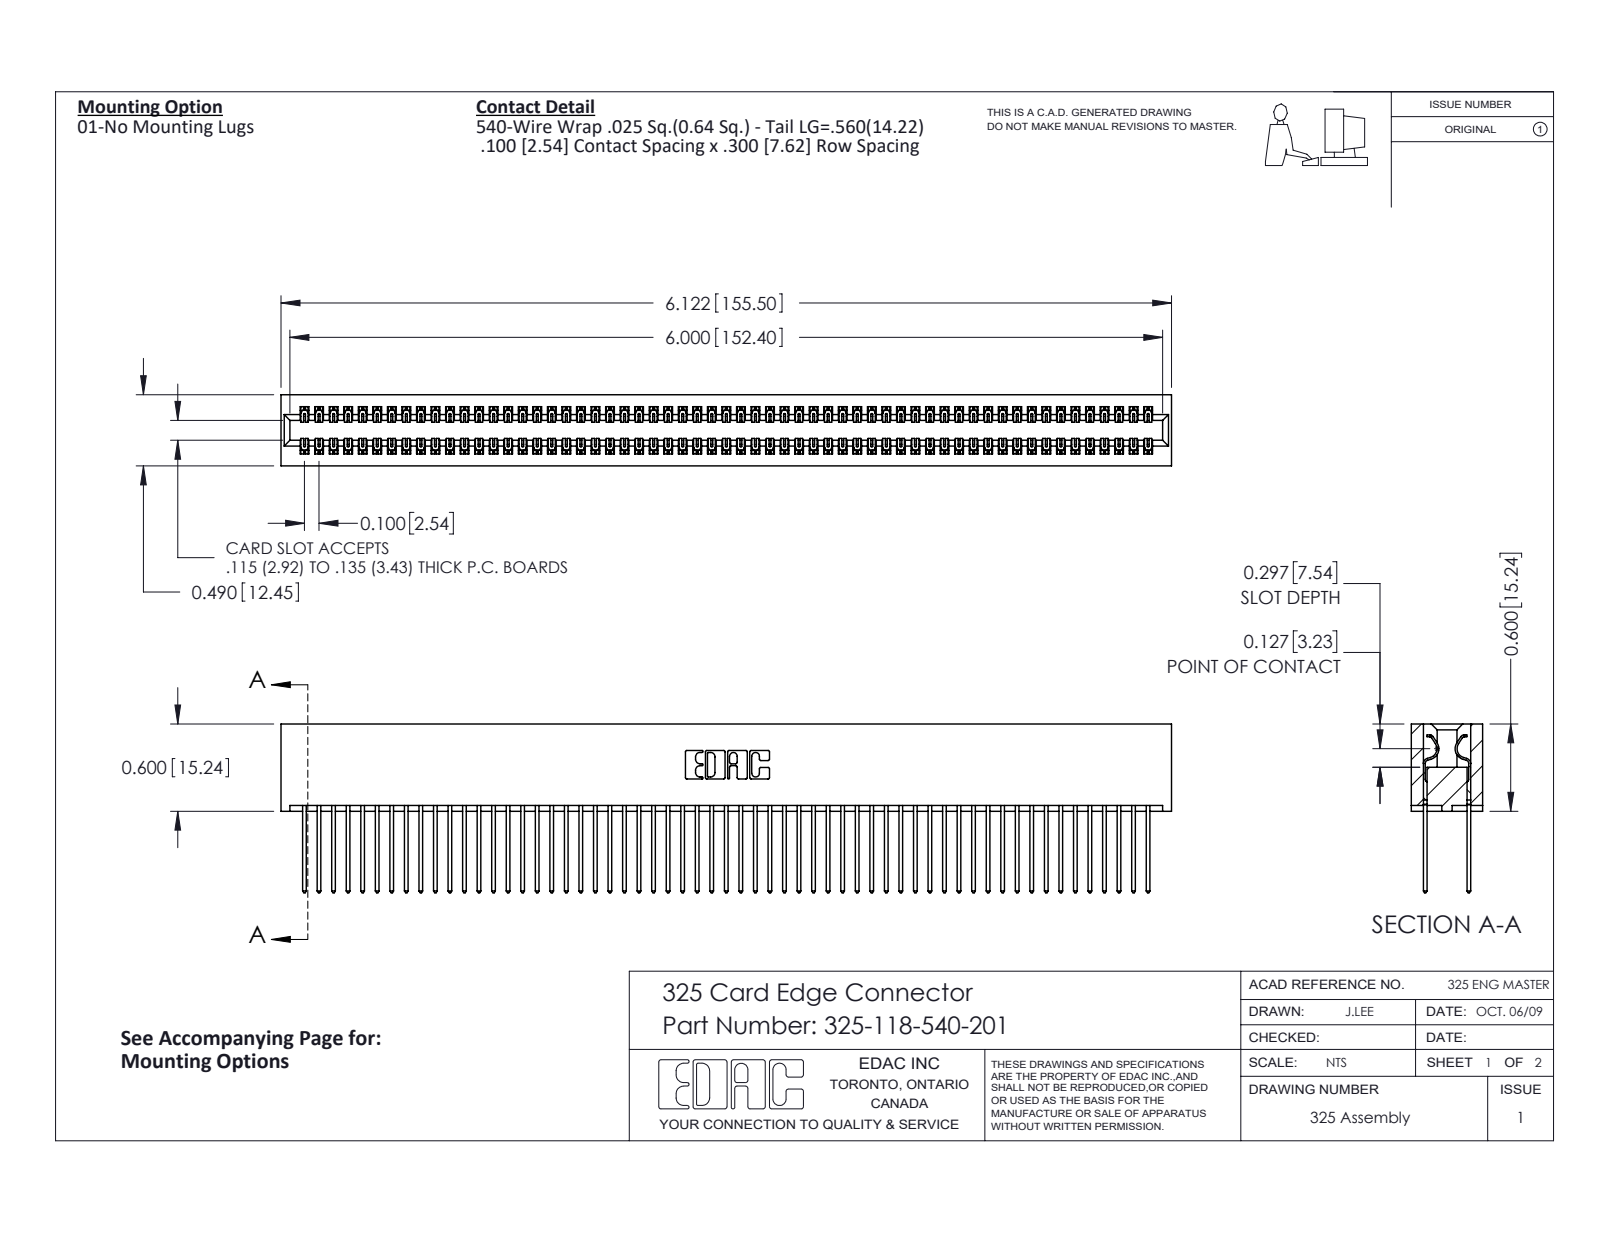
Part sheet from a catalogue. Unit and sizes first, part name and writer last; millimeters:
Units: millimetres
Overall size (bounding box): 155.5 × 29.5 × 12.4
Partial cylindrical surfaces — rounded edges, fillets, slot ends (radius × count): R0.2 ×177, R0.3 ×118, R0.3 ×22, R0.2 ×6, R0.8 ×6, R0.7 ×3, R0.4 ×2, R0.6 ×2
Main face-to-face distances: 2.1, 10.3, 7.6, 2.7, 9.7, 0.6, 8.3, 12.4, 7, 14.2
Volume: 21 290 mm³ · Surface area: 28 950 mm²
Bodies: 119 solids, 6242 faces (4314 planar, 1928 cylindrical, 0 other)
Part name (STEP PRODUCT): 325-118-540-201; 325 Part_Lugless; 325-292-001_325-293-140
STEP written by: SolidWorks 2016 (CONFIG_CONTROL_DESIGN)
